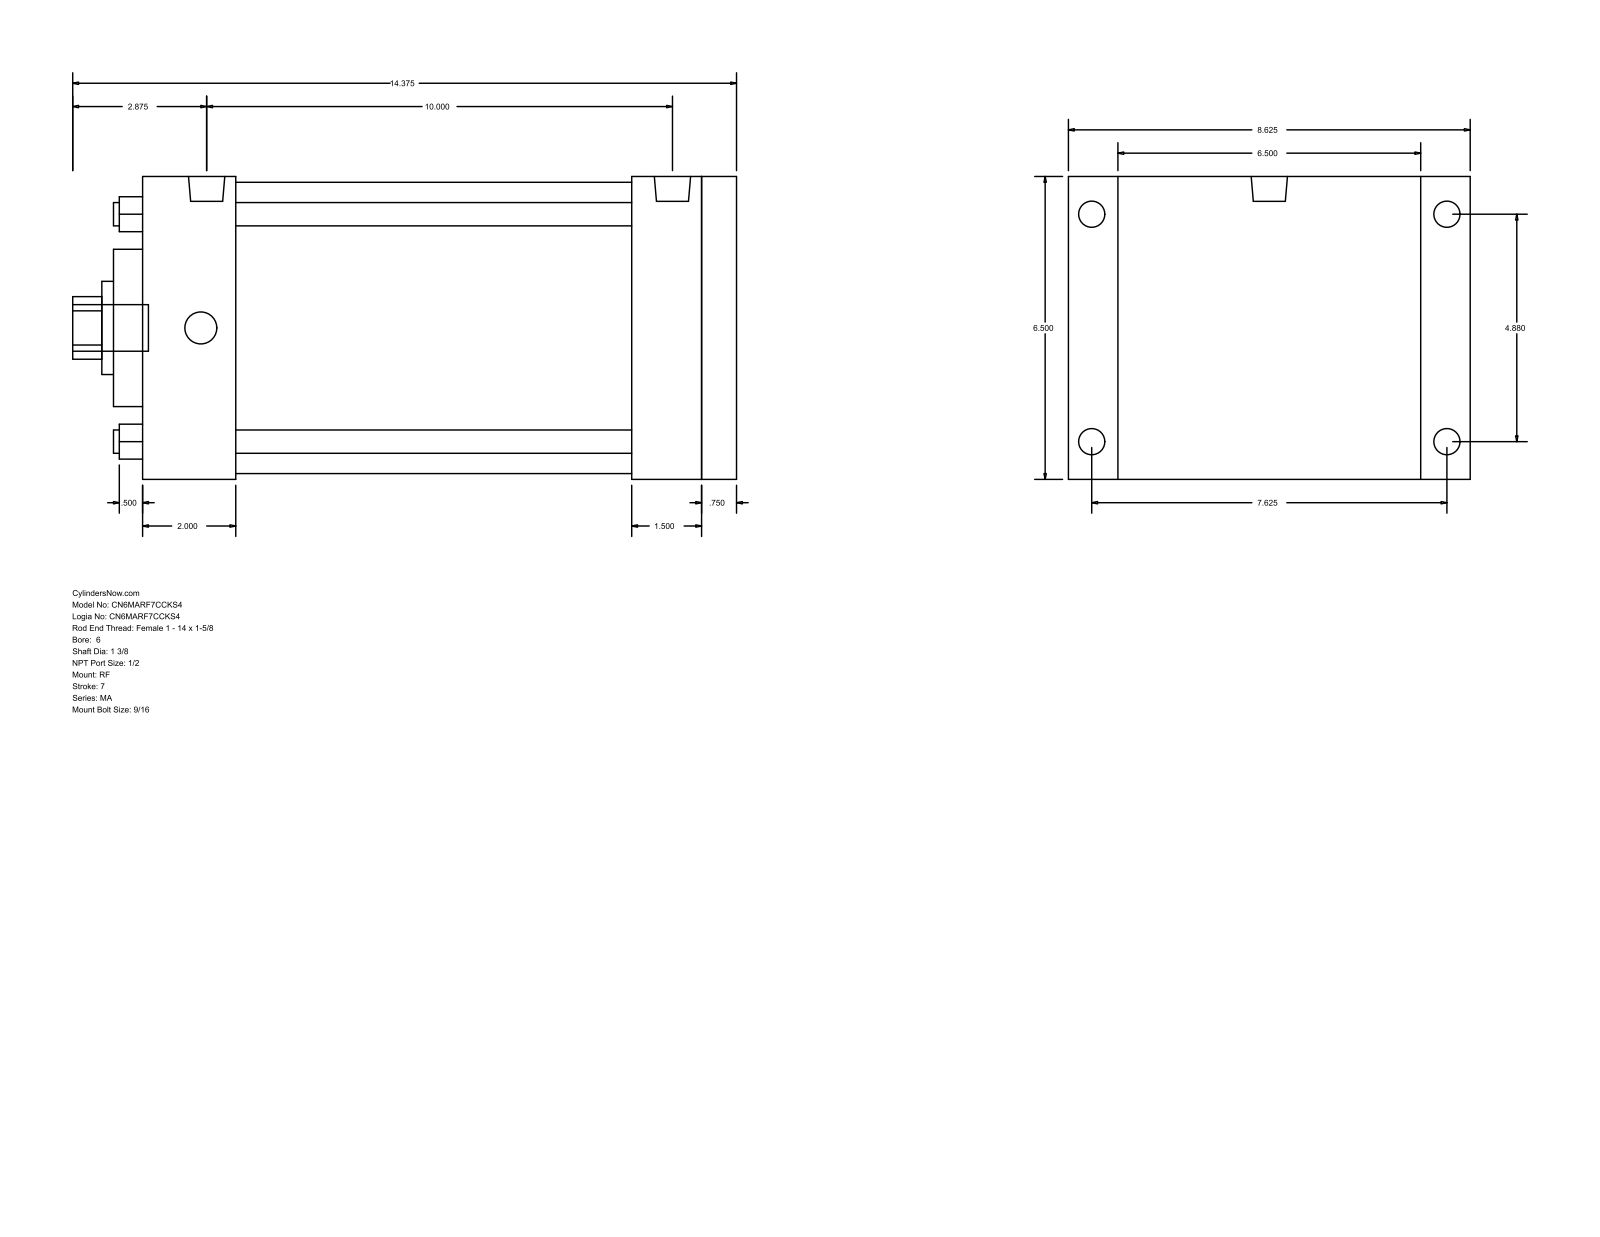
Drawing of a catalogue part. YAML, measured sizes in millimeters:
part_name: "MA_RF__0600_1.375"
step_written_by: "GSSL Pune (CONFIG_CONTROL_DESIGN)"
units: millimeters
bodies: {solids: 0, faces: 94, planar: 65, cylindrical: 29, other: 0}
overall_size: [365.12, 219.07, 165.1]
round_holes:
  - {diameter: 12.7, count: 4}
  - {diameter: 34.92, count: 1}
  - {diameter: 50.8, count: 1}
  - {diameter: 85.72, count: 1}
  - {diameter: 158.75, count: 1}
round_bosses_or_shafts:
  - {diameter: 17.46, count: 4}
  - {diameter: 14.29, count: 4}
  - {diameter: 19.77, count: 2}
  - {diameter: 25.4, count: 1}
partial_cylinders:
  - {radius: 17.06, count: 1}
face_to_face_distances: [165.1, 327.02, 219.08, 19.05, 307.97, 50.8, 257.17, 276.22, 269.88, 38.09]
hole_center_spacings: [87.65, 123.96, 175.31]
